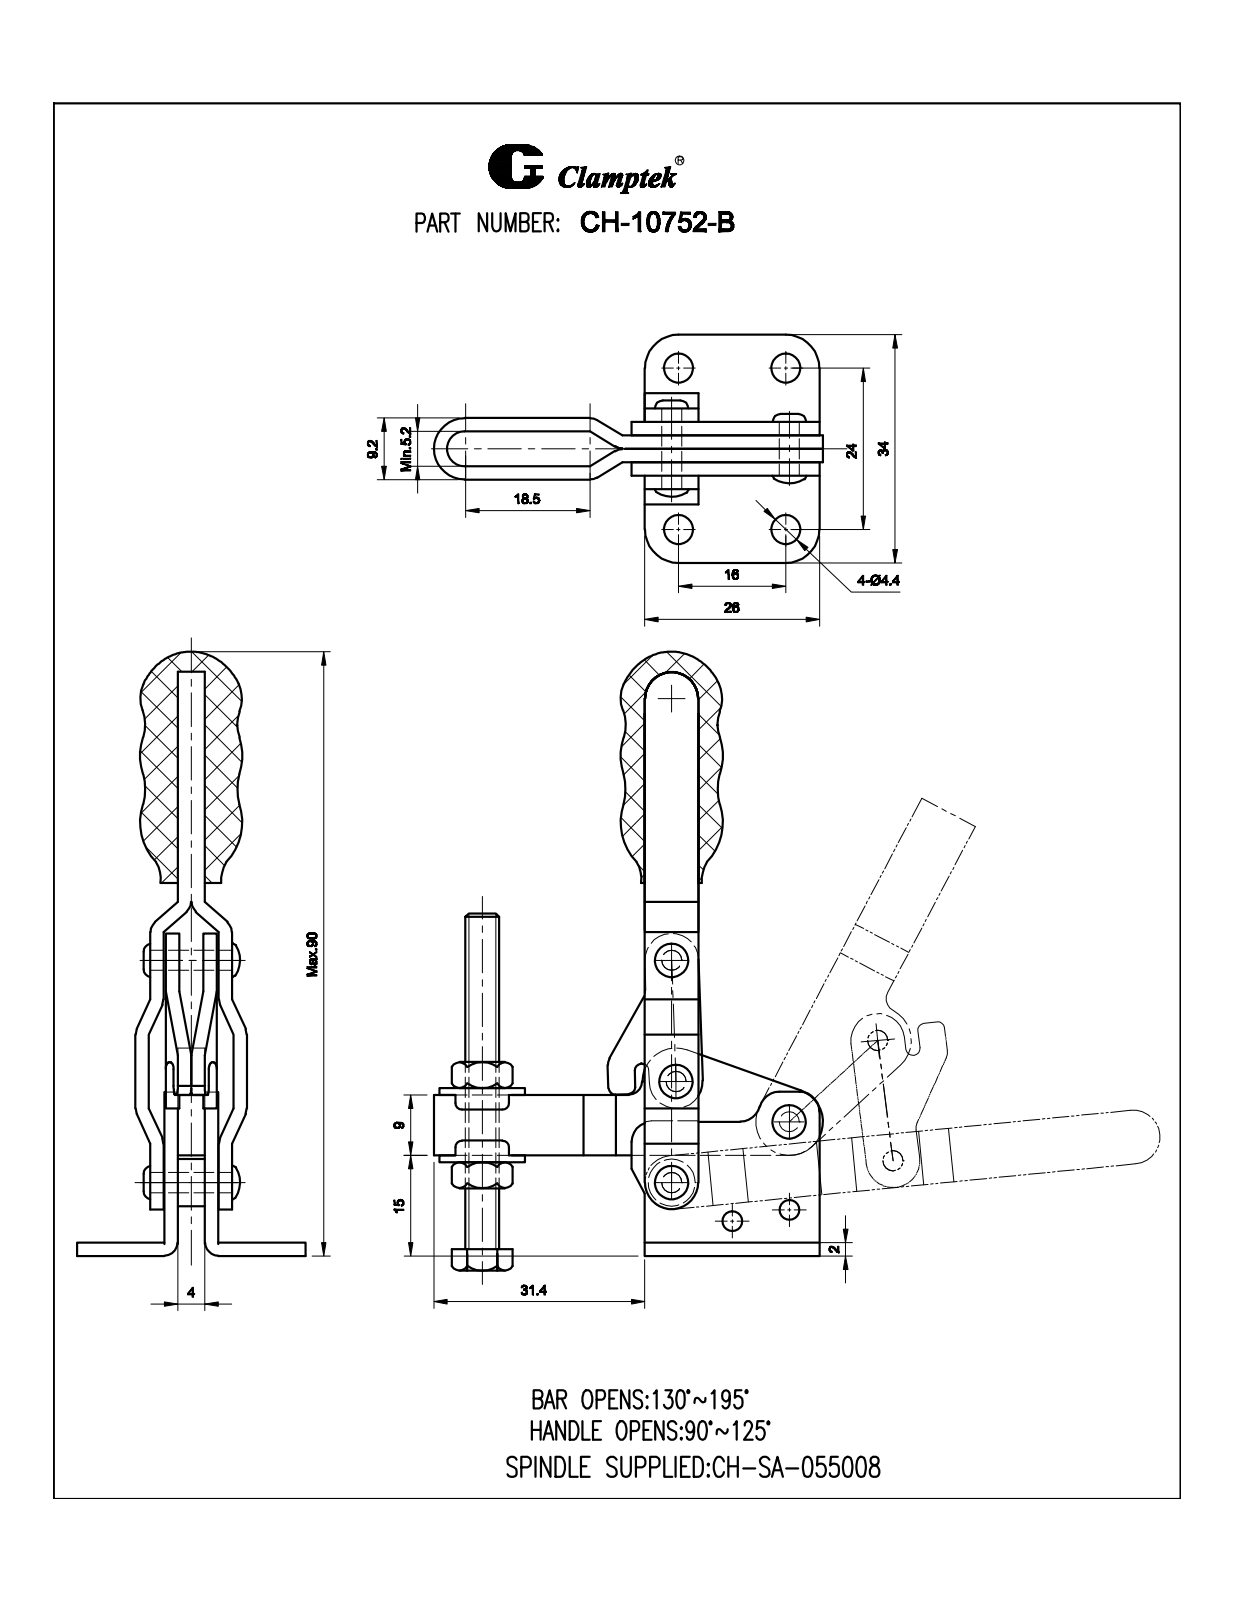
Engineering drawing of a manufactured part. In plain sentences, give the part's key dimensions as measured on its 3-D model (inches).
The part is named "CH-10752-B-06; M5 Nut; CH-SA-055008 SPINDLE SUPPLIED; CH-10752-B-09 (+8 more)". Its 3-D file was written by "SolidWorks 2010 (CONFIG_CONTROL_DESIGN)". It is 21 solids with 907 faces: 330 planar, 307 cylindrical and 270 other. Overall it measures 3.967 by 2.264 by 1.339 inches. Its volume is 0.816 cubic inches and its surface area 27.08 square inches. Round holes: 4 of diameter 0.157, 4 of diameter 0.173, 2 of diameter 0.118, 1 of diameter 0.031, 1 of diameter 0.079, 1 of diameter 0.165, 1 of diameter 0.193. Round bosses or shafts: 1 of diameter 0.276, 1 of diameter 0.197, 1 of diameter 0.028. Partial cylindrical surfaces (rounded edges, fillets, slot ends): 24 of radius 0.079, 9 of radius 0.039, 6 of radius 0.197, 4 of radius 0.03, 4 of radius 0.118, 4 of radius 0.157, 1 of radius 0.108, 1 of radius 0.187. The main face-to-face distances are 0.079, 0.157, 0.236, 0.083, 0.075, 0.161, 0.315, 0.154, 0.24, 0.087. The hole center spacings are 0.63, 0.945, 1.135, 0.341, 0.42, 0.516, 0.592, 0.672.
